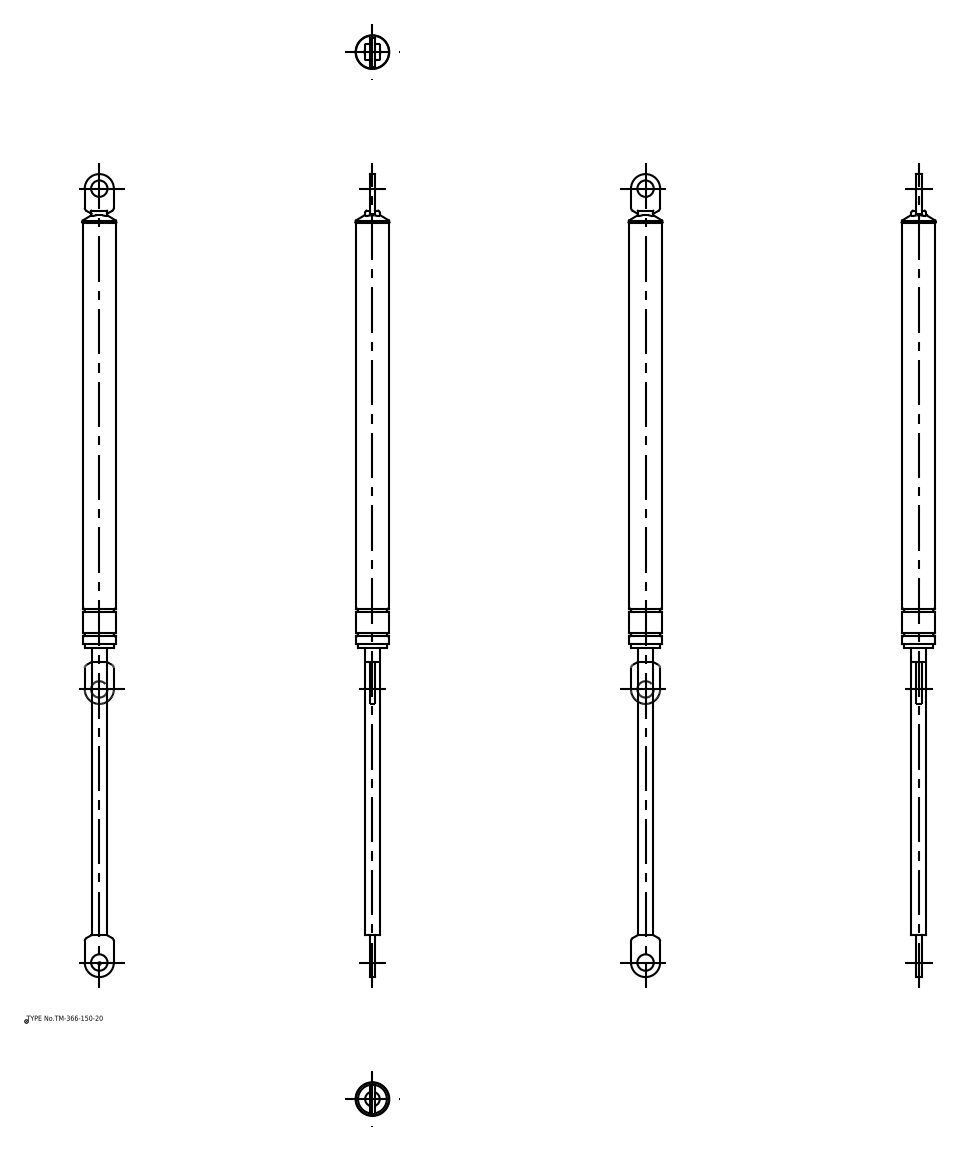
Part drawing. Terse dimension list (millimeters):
name: TM_366_150_20; TM_366_150_20_div
written by: spGate 16.7.1 (AUTOMOTIVE_DESIGN)
unit: mm
bodies: 2 solids, 89 faces (35 planar, 36 cylindrical, 18 other)
size: 441 × 18.5 × 18.5
volume: 69 571 mm³; area: 19 591 mm²
holes: 2× ⌀9
bosses: 1× ⌀18, 1× ⌀15.8, 1× ⌀8
rounds: 8× R0.3, 4× R2, 2× R0.5, 2× R1.15, 2× R8
face distances: 3.2, 16, 1.7, 158, 159.7, 3.7, 12.3, 13.5, 1.8, 2.4
hole spacings: 425
